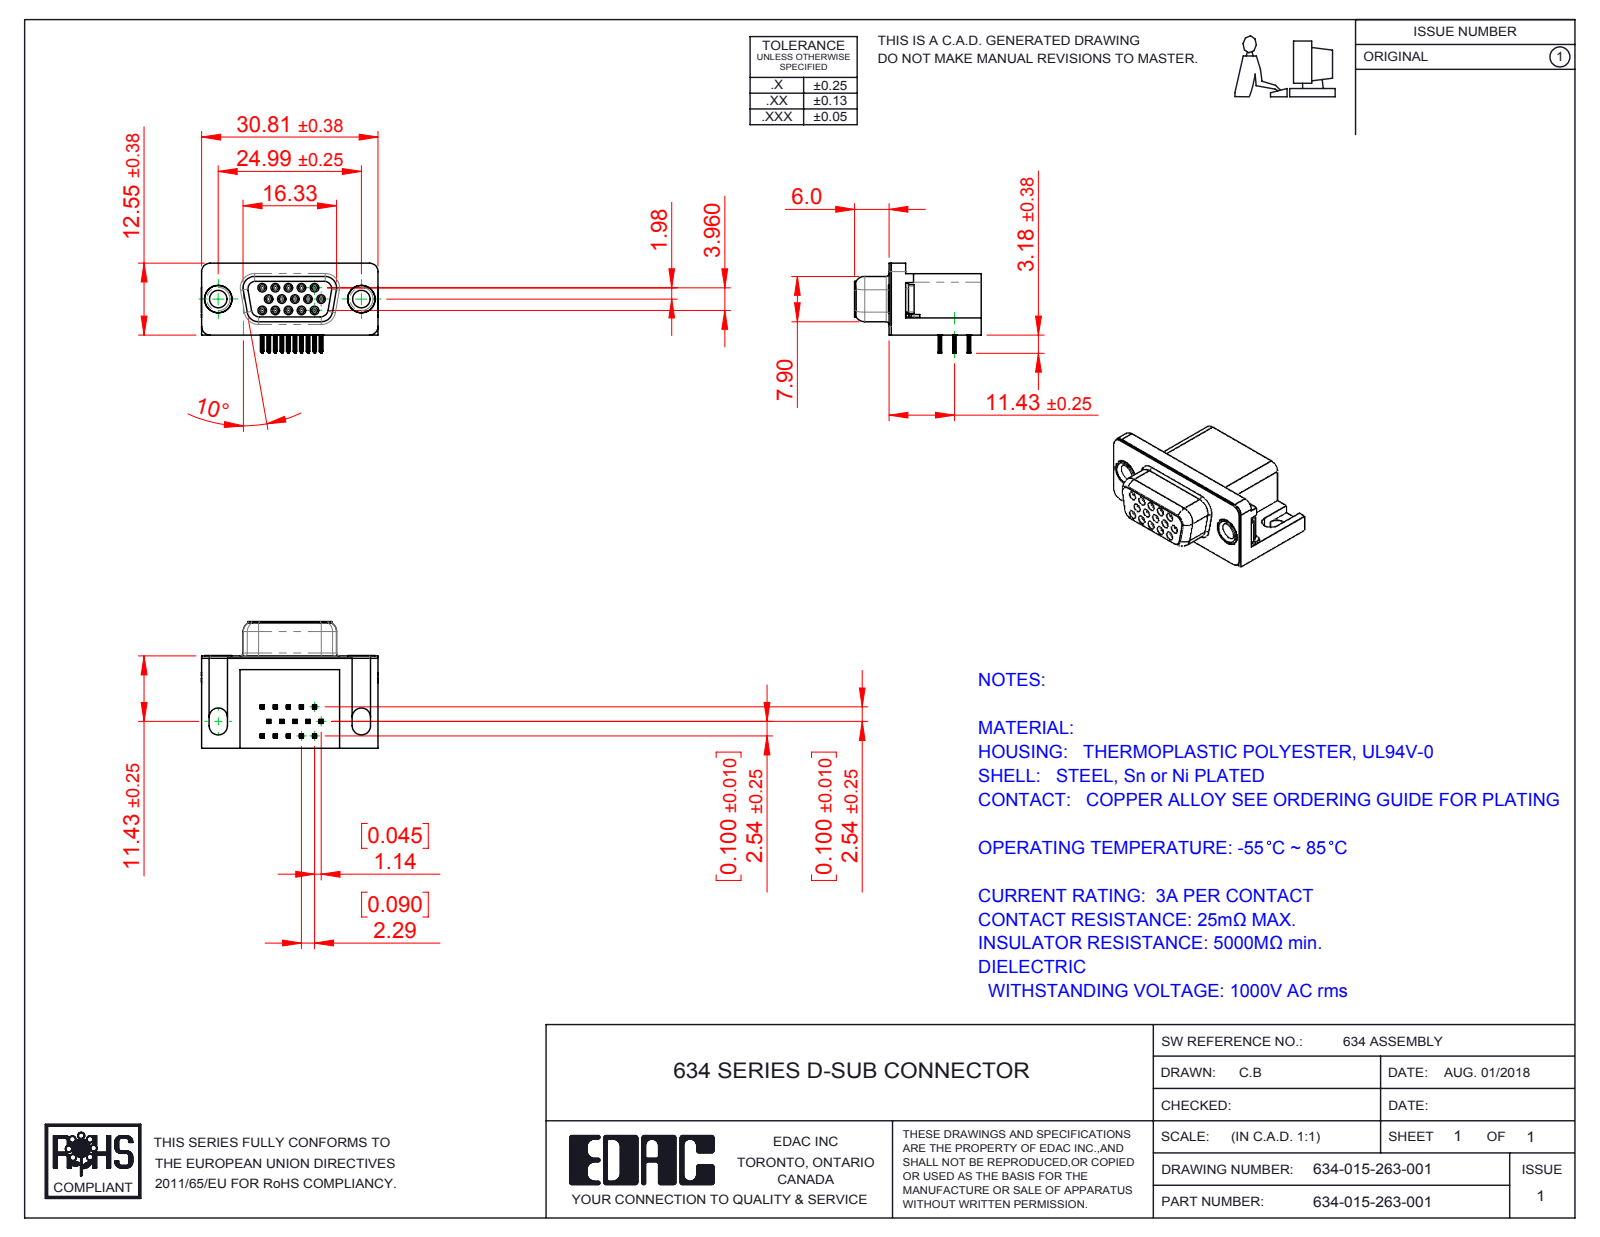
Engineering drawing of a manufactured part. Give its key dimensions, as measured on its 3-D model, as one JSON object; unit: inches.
{"part_name": "Contact Middle; 634 Housing; Thru Hole Rivet; Contact Bottom (+4 more)", "step_written_by": "SolidWorks 2016 (CONFIG_CONTROL_DESIGN)", "units": "inches", "bodies": {"solids": 21, "faces": 2377, "planar": 1066, "cylindrical": 577, "other": 734}, "overall_size": [1.216, 0.87, 0.619], "volume_in3": 0.274, "surface_area_in2": 9.701, "round_holes": [[0.031, 15], [0.035, 15], [0.12, 2], [0.157, 2], [0.189, 2], [0.197, 2]], "round_bosses_or_shafts": [[0.047, 15], [0.193, 2], [0.187, 2], [0.152, 2]], "partial_cylinders_radius": [[0.004, 120], [0.006, 60], [0.014, 30], [0.039, 19], [0.013, 15], [0.01, 8], [0.053, 8], [0.063, 8]], "face_to_face_distances": [0.016, 0.407, 0.618, 0.634, 0.098, 0.264, 0.114, 0.252, 0.014, 0.421], "hole_center_spacings": [0.09, 0.09, 0.156, 0.18, 0.238, 0.156, 0.18, 0.27]}
